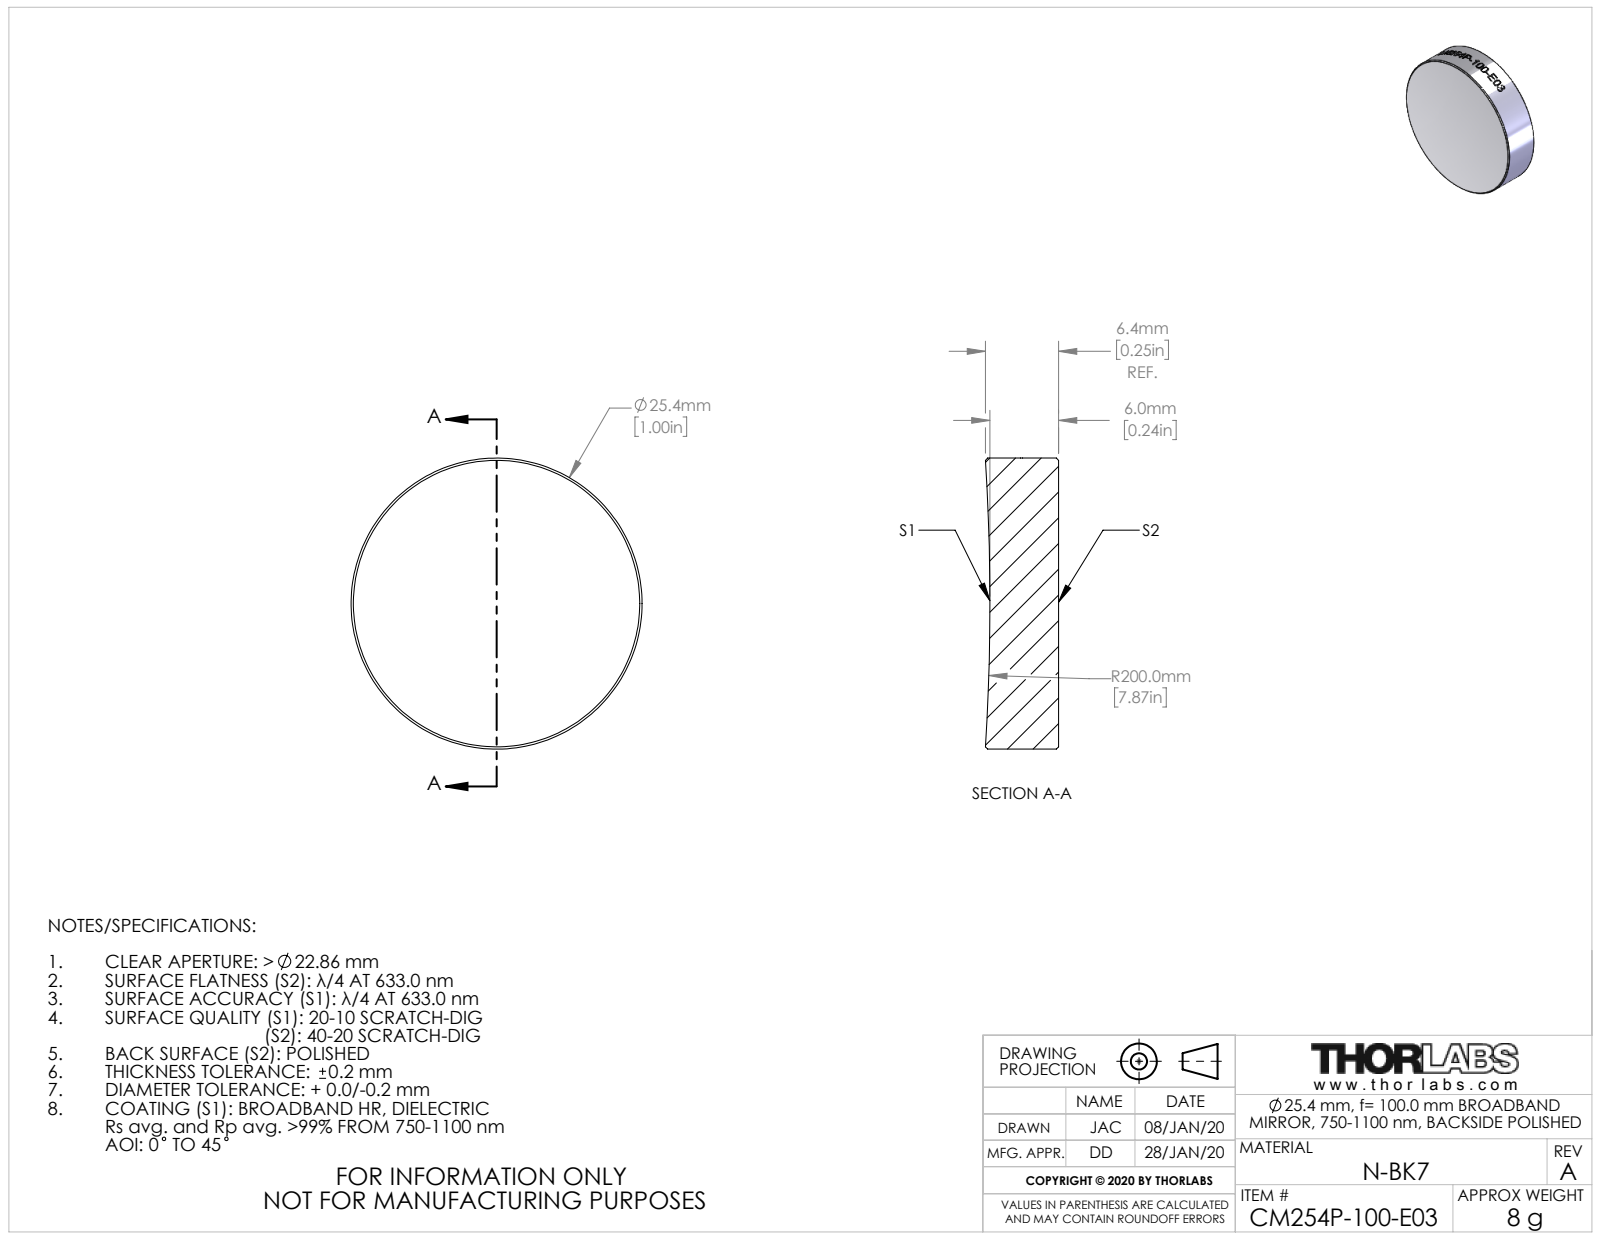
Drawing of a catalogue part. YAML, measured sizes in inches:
part_name: "TTN201402-E0W"
step_written_by: "SolidWorks 2018 (CONFIG_CONTROL_DESIGN)"
units: inches
bodies: {solids: 1, faces: 28, planar: 1, cylindrical: 21, other: 6}
overall_size: [1, 1, 0.252]
volume: 0.192
surface_area: 2.333
round_bosses_or_shafts:
  - {diameter: 1, count: 1}
